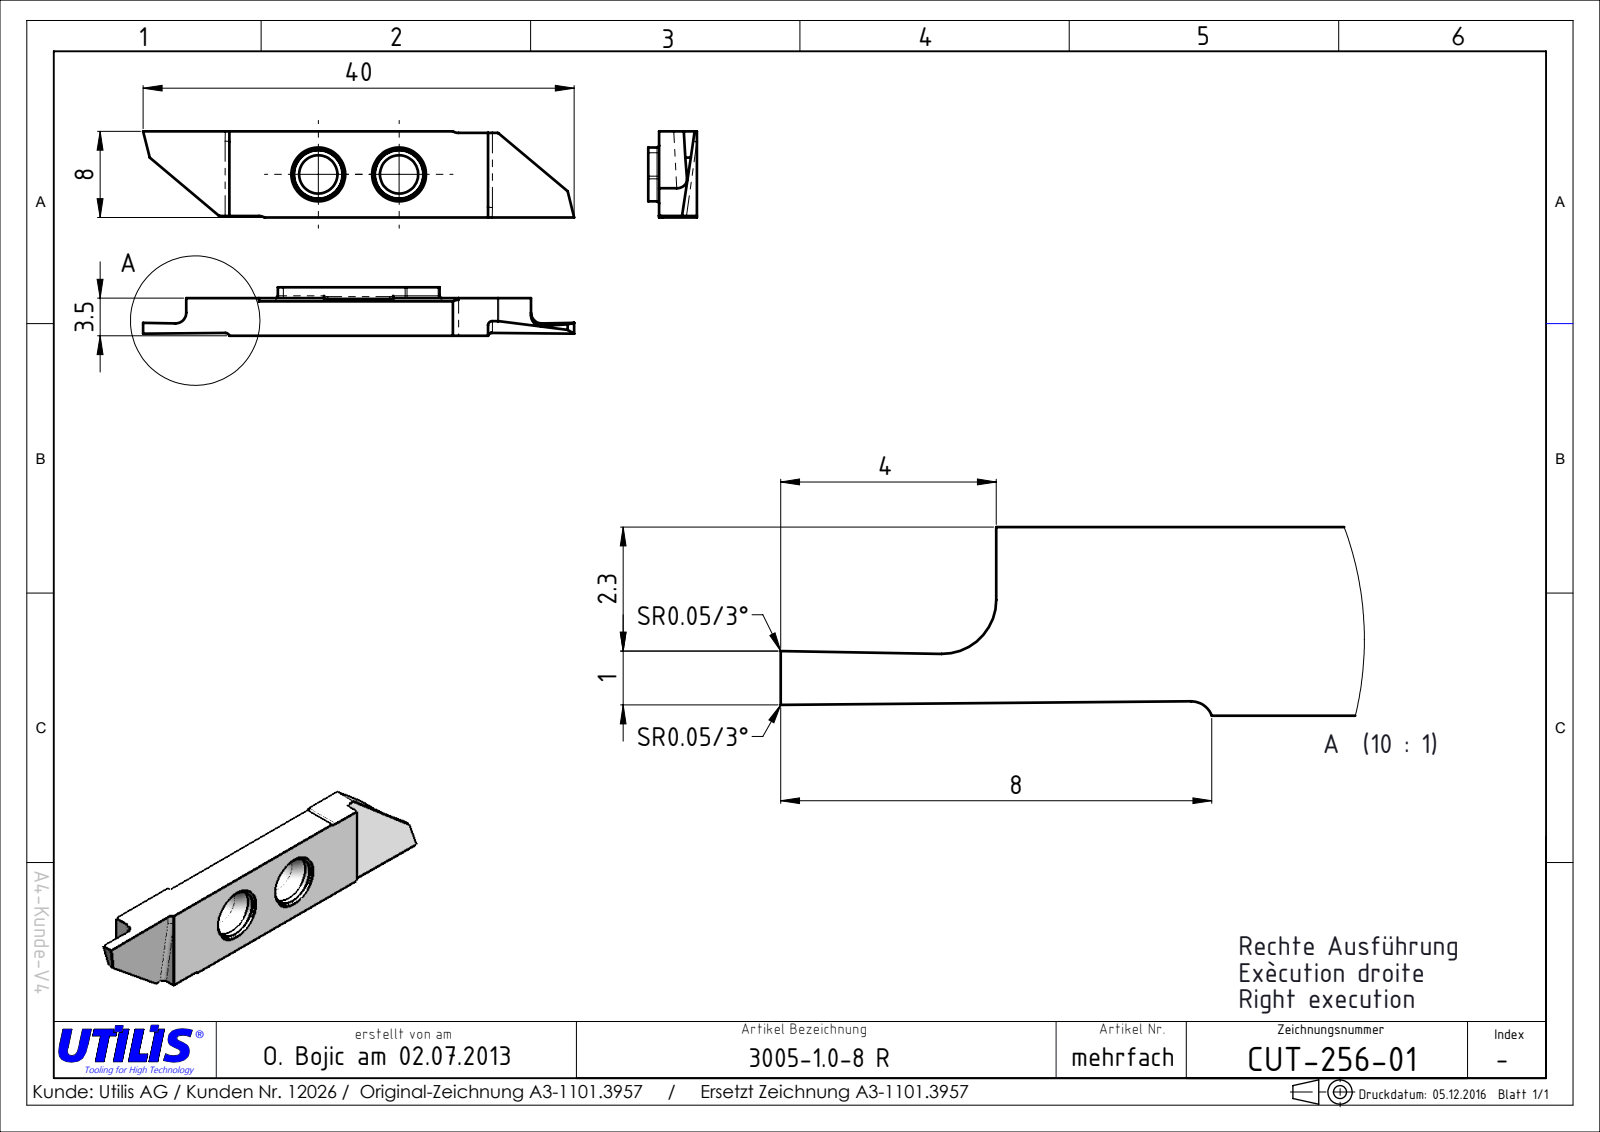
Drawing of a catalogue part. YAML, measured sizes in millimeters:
part_name: "CUT-256-01"
step_written_by: "SolidWorks 2016 (AUTOMOTIVE_DESIGN)"
units: millimeters
bodies: {solids: 1, faces: 38, planar: 24, cylindrical: 14, other: 0}
overall_size: [40, 8, 3.5]
volume: 806
surface_area: 852
round_holes:
  - {diameter: 3.55, count: 2}
partial_cylinders:
  - {radius: 0.15, count: 4}
  - {radius: 1, count: 4}
  - {radius: 0.4, count: 2}
face_to_face_distances: [3.5, 8, 7.85, 22.54, 7.7, 32, 4, 36, 40, 38.98]
hole_center_spacings: [7.5]
